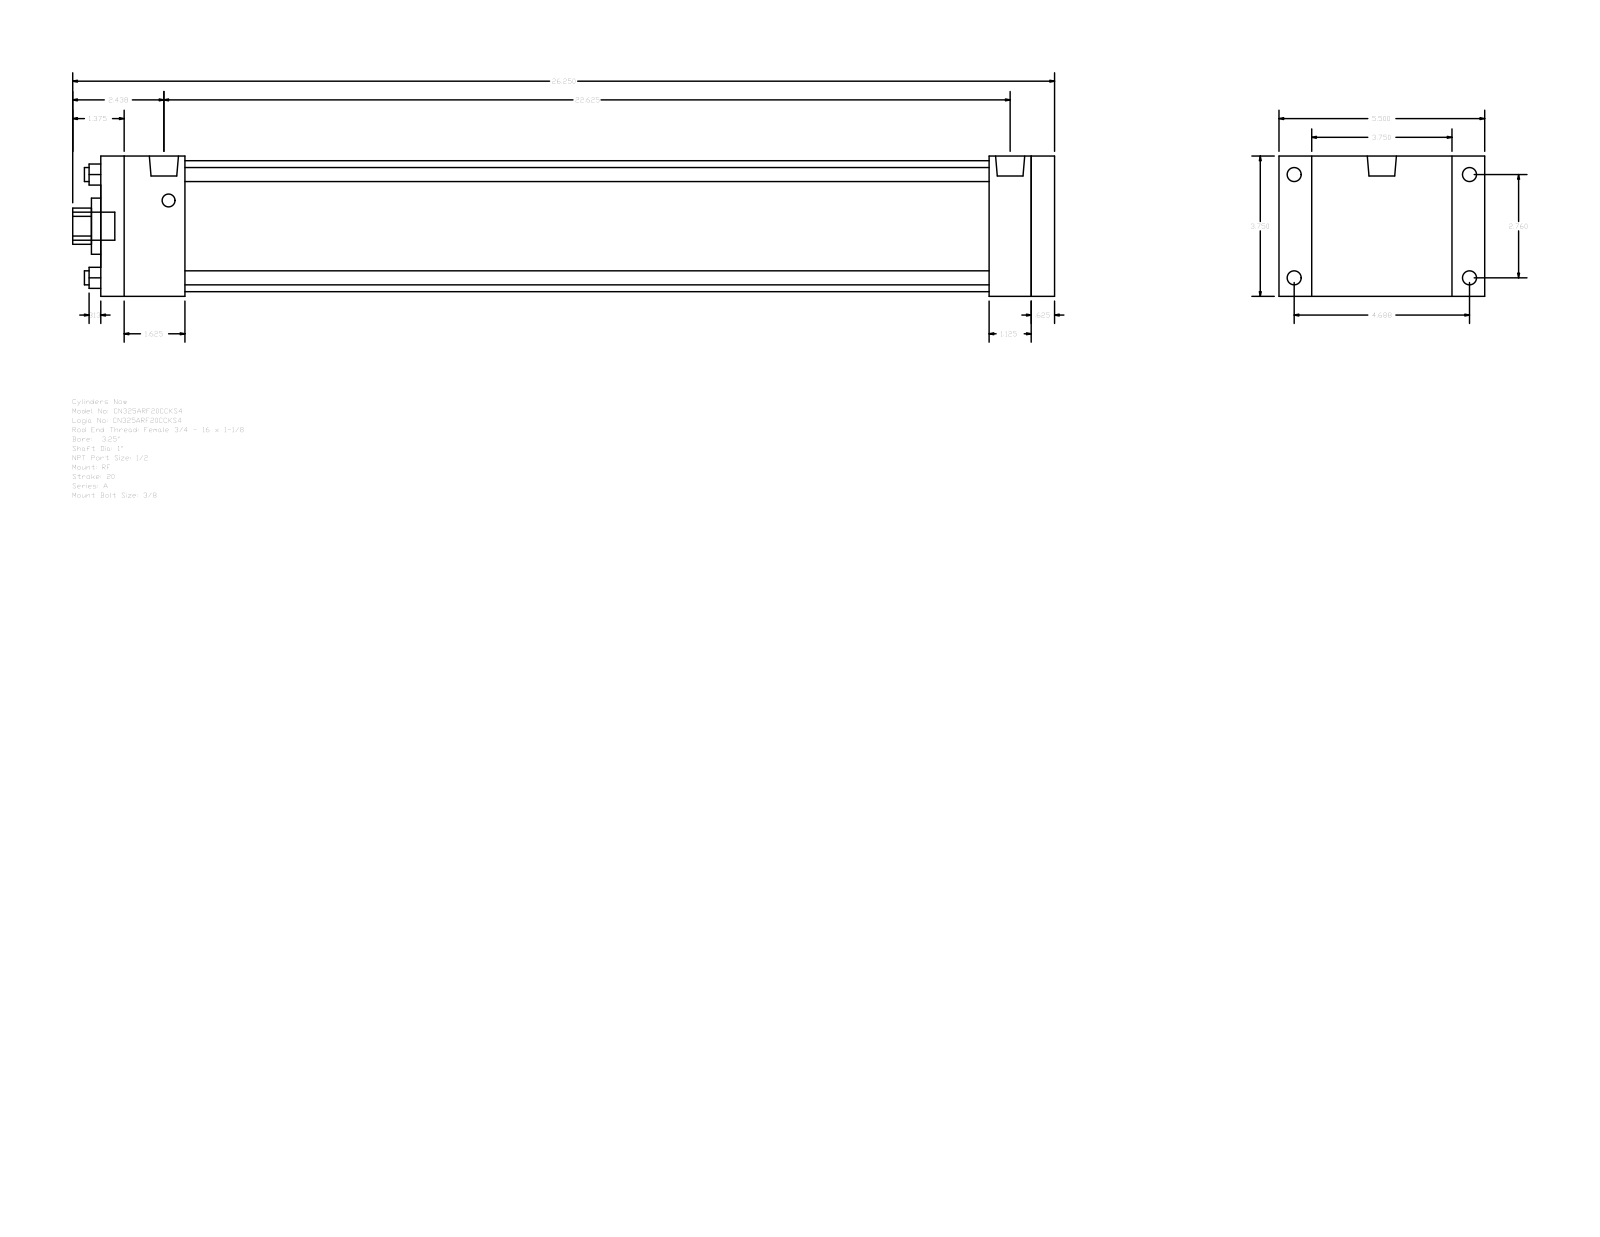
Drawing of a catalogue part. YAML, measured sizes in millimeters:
part_name: "A_RF__0325_1"
step_written_by: "GSSL Pune (CONFIG_CONTROL_DESIGN)"
units: millimeters
bodies: {solids: 0, faces: 92, planar: 64, cylindrical: 28, other: 0}
overall_size: [666.75, 139.7, 95.25]
round_holes:
  - {diameter: 9.53, count: 4}
  - {diameter: 25.4, count: 1}
  - {diameter: 38.1, count: 1}
  - {diameter: 88.9, count: 1}
round_bosses_or_shafts:
  - {diameter: 9.53, count: 4}
  - {diameter: 8.73, count: 4}
  - {diameter: 19.77, count: 2}
  - {diameter: 19.05, count: 1}
partial_cylinders:
  - {radius: 12.29, count: 1}
face_to_face_distances: [95.24, 647.7, 15.87, 631.83, 22.23, 117.47, 603.25, 28.58, 44.45, 57.15]
hole_center_spacings: [49.57, 70.1, 99.14]
